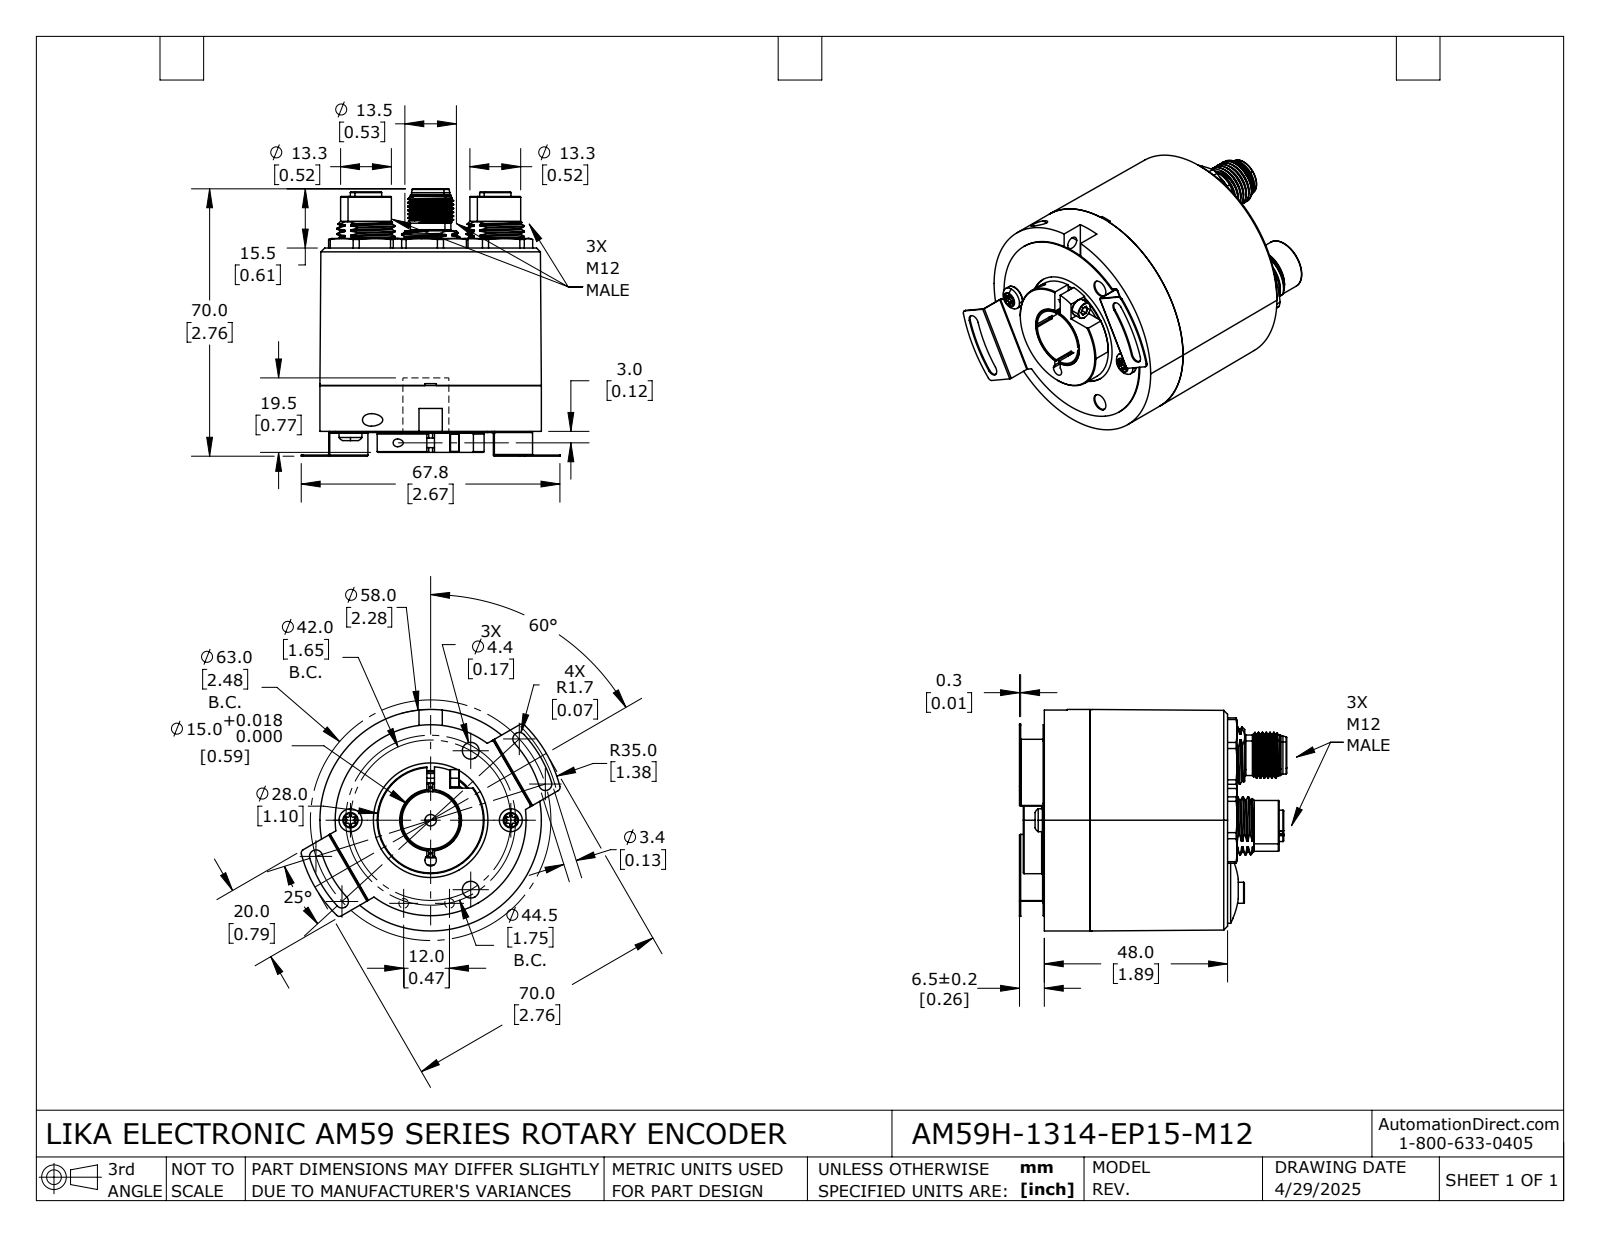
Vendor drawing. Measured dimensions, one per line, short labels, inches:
name: AM59H-1314-EP15-M12
written by: SolidWorks 2024 (AUTOMOTIVE_DESIGN)
unit: in
bodies: 55 solids, 1648 faces (438 planar, 595 cylindrical, 615 other)
size: 2.756 × 2.669 × 2.283
volume: 3.965 in³; area: 84.73 in²
holes: 11× ⌀0.079, 10× ⌀0.047, 8× ⌀0.098, 6× ⌀0.081, 5× ⌀0.138, 4× ⌀0.063, 3× ⌀0.492, 2× ⌀0.126, 2× ⌀0.173, 2× ⌀0.382, 2× ⌀0.429, 1× ⌀0.041
bosses: 12× ⌀0.063, 12× ⌀0.039, 8× ⌀0.118, 3× ⌀0.524, 3× ⌀0.236, 1× ⌀2.283, 1× ⌀2.185, 1× ⌀2.165
rounds: 29× R0.039, 26× R0.008, 12× R0.01, 12× R0.017, 6× R0.004, 4× R0.006, 4× R0.012, 4× R0.067
face distances: 0.098, 1.791, 1.89, 1.902, 1.803, 0.602, 1.299, 0.02, 0.787, 0.689
hole spacings: 0.827, 0.209, 0.295, 0.591, 0.791, 0.835, 0.965, 1.27
